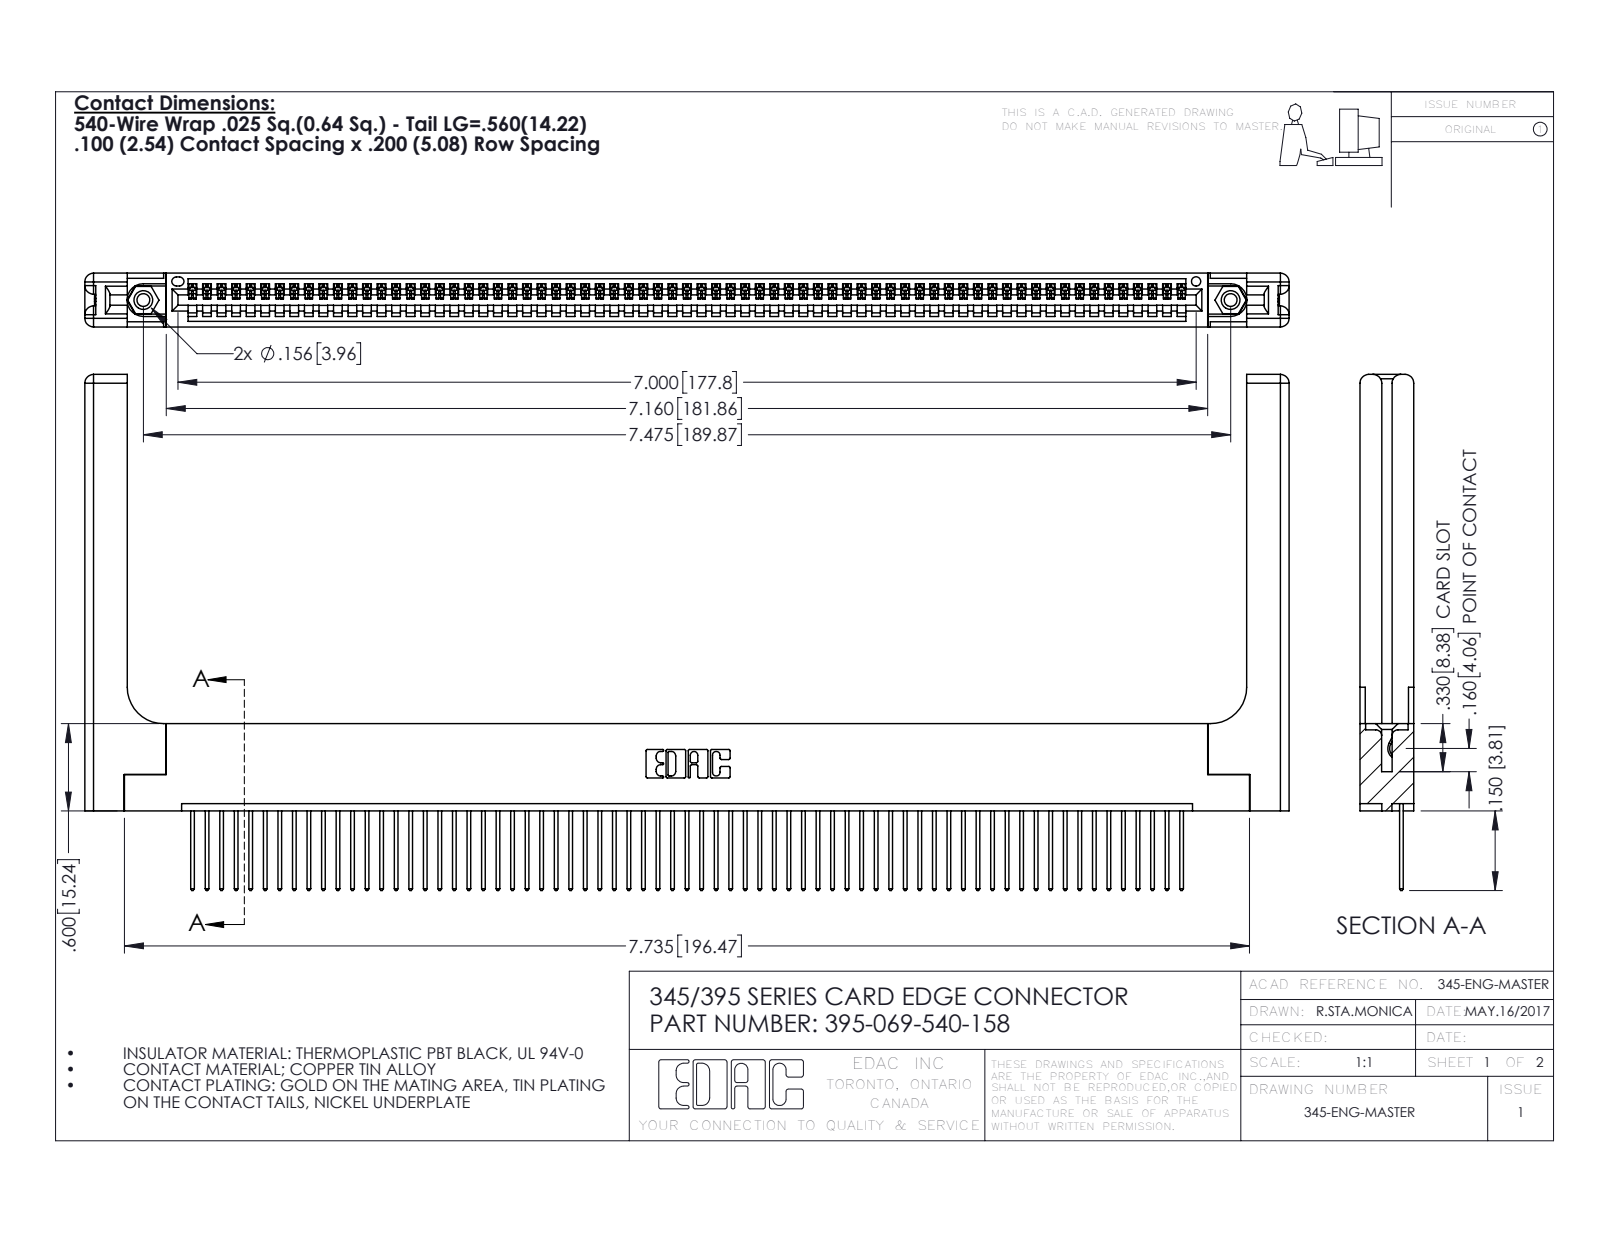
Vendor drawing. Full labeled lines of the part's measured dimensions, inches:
Part name (STEP PRODUCT): 345-220-058_345-220-058; 395-069-540-158; 345-292-001_345-293-140; 345 Part_Flush Mounting Lugs - 0.156 Dia-TH (+1 more)
STEP written by: SolidWorks 2016 (CONFIG_CONTROL_DESIGN)
Units: inches
Bodies: 74 solids, 4384 faces (2988 planar, 1336 cylindrical, 60 other)
Overall size (bounding box): 8.279 × 3.547 × 0.37
Volume: 1.757 in³ · Surface area: 51.62 in²
Round holes (diameter × count): ⌀0.089 ×2, ⌀0.125 ×2, ⌀0.156 ×2, ⌀0.064 ×1
Round bosses / shafts (diameter × count): ⌀0.155 ×2
Partial cylindrical surfaces — rounded edges, fillets, slot ends (radius × count): R0.006 ×138, R0.01 ×138, R0.01 ×22, R0.06 ×16, R0.007 ×6, R0.031 ×6, R0.026 ×3, R0.03 ×2
Main face-to-face distances: 0.072, 0.298, 0.37, 0.098, 0.272, 0.025, 0.2, 0.225, 0.148, 0.15
Hole centre spacings: 0.27, 7.239, 7.475
